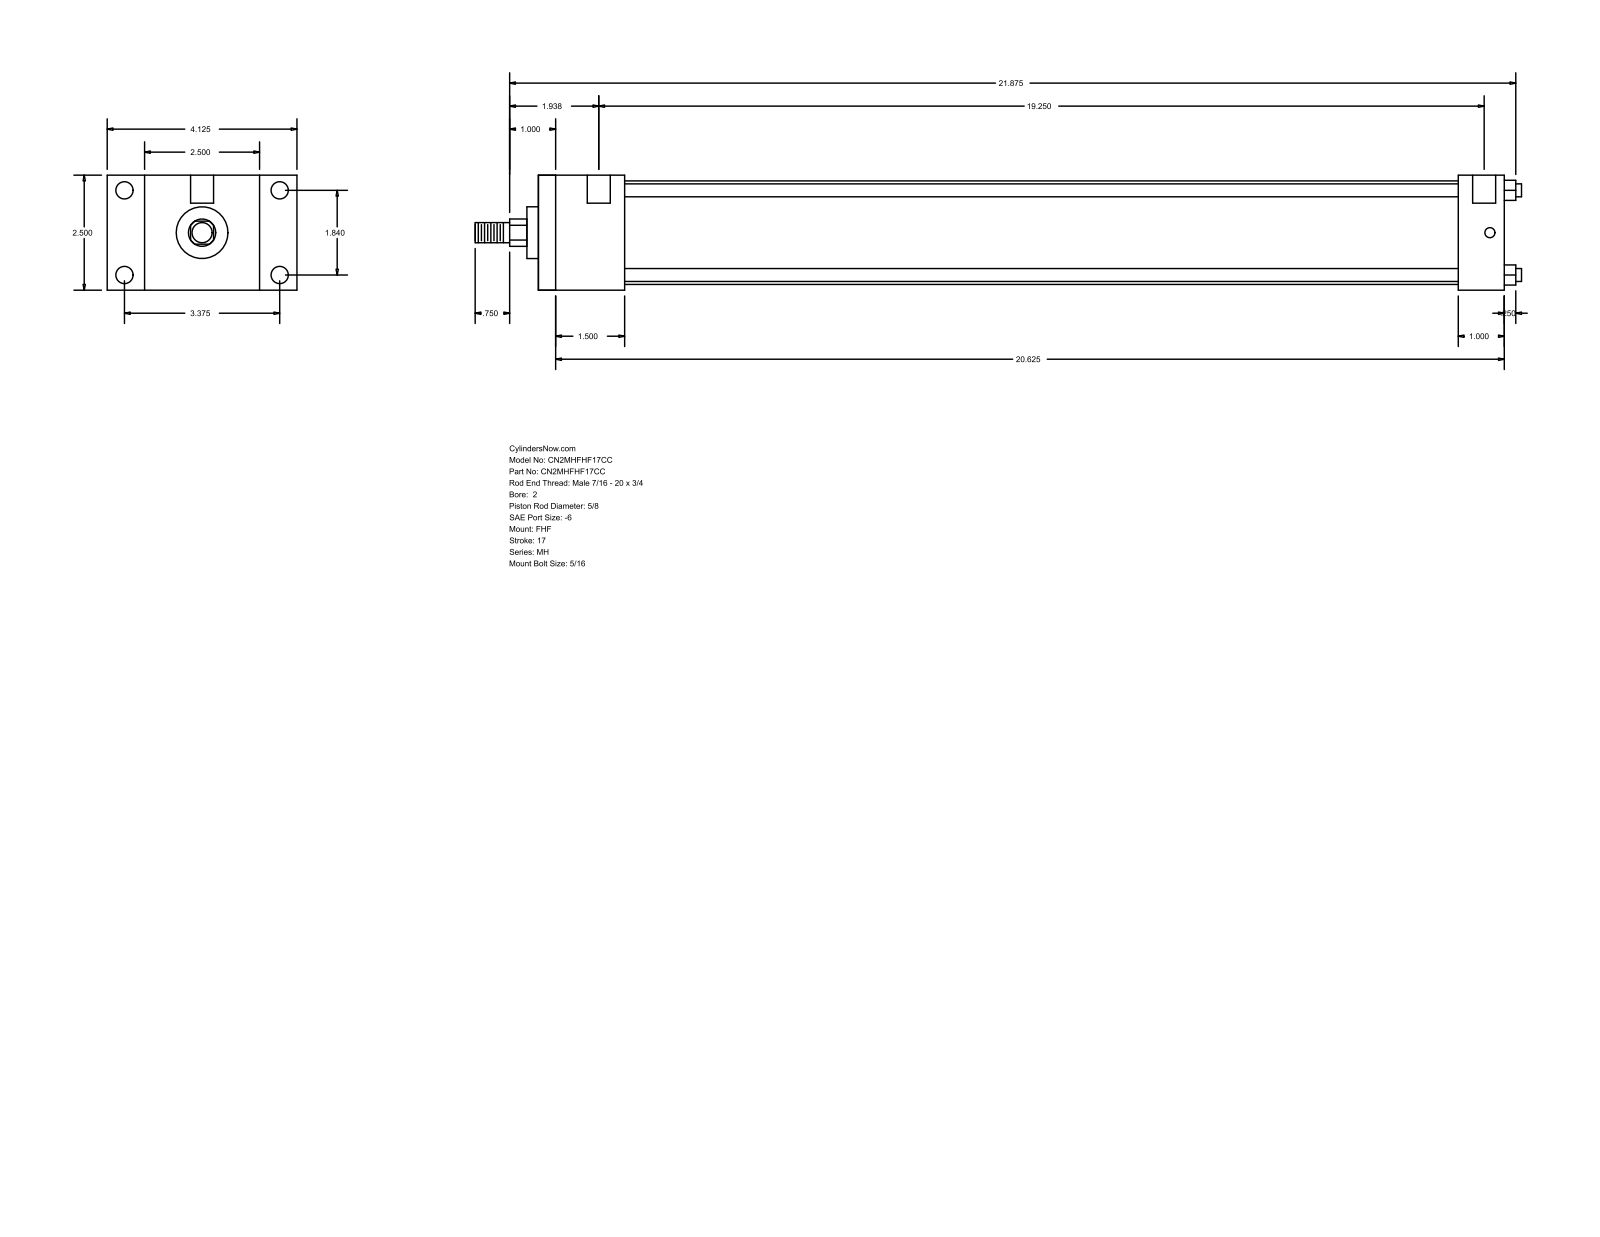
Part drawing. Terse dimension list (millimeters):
name: MH_FHF__0200_0.625
written by: GSSL Pune (CONFIG_CONTROL_DESIGN)
unit: mm
bodies: 0 solids, 88 faces (60 planar, 28 cylindrical, 0 other)
size: 577.85 × 104.78 × 63.5
holes: 4× ⌀5.56, 4× ⌀9.53, 2× ⌀12.7
bosses: 4× ⌀7.14, 1× ⌀57.15, 1× ⌀28.57, 1× ⌀15.88, 1× ⌀11.11
rounds: 1× R7.54
face distances: 63.5, 47.62, 533.39, 485.77, 20.64, 84.14, 104.78, 508, 460.38, 25.39
hole spacings: 46.74, 85.72, 97.63, 496.89, 3.18, 4.76, 488.95, 492.13
